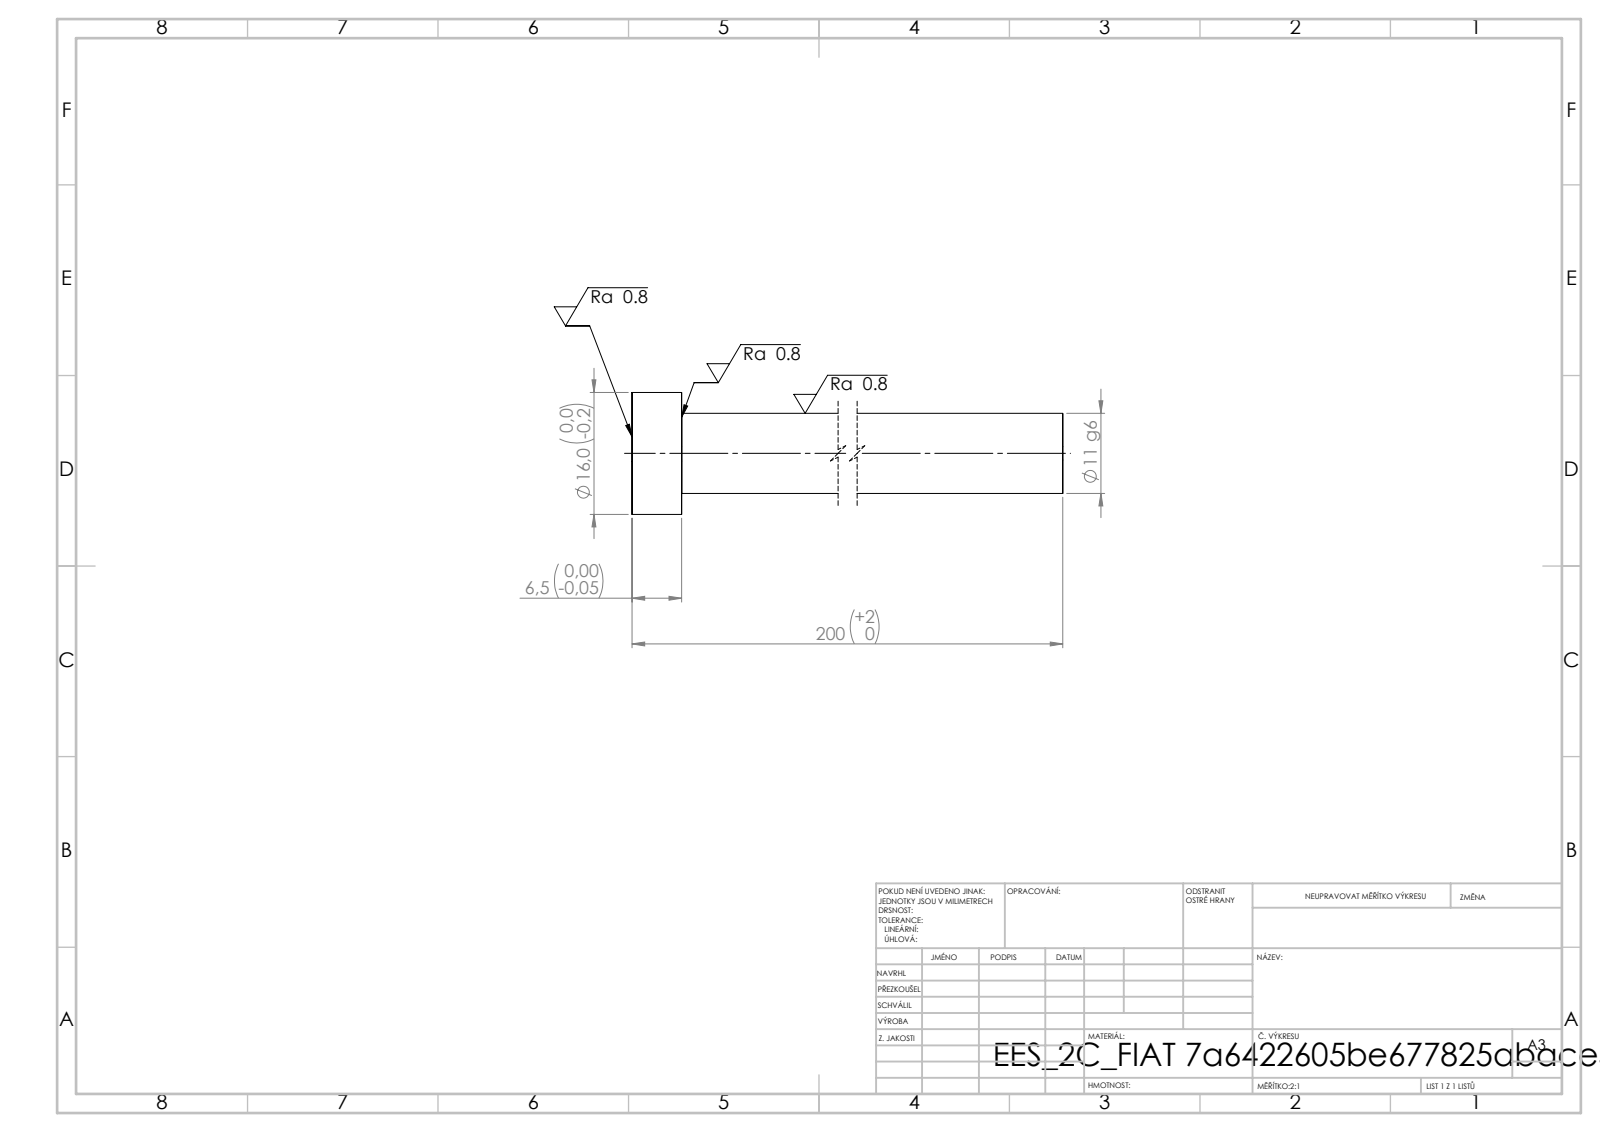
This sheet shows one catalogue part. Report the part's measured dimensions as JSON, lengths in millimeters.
{"step_written_by": "SolidWorks 2019 (CONFIG_CONTROL_DESIGN)", "units": "millimeters", "bodies": {"solids": 1, "faces": 7, "planar": 3, "cylindrical": 4, "other": 0}, "overall_size": [200, 16, 16], "volume_mm3": 18062, "surface_area_mm2": 7112, "round_bosses_or_shafts": [[16, 1], [10.5, 1]], "face_to_face_distances": [6.5, 200, 193.5]}
